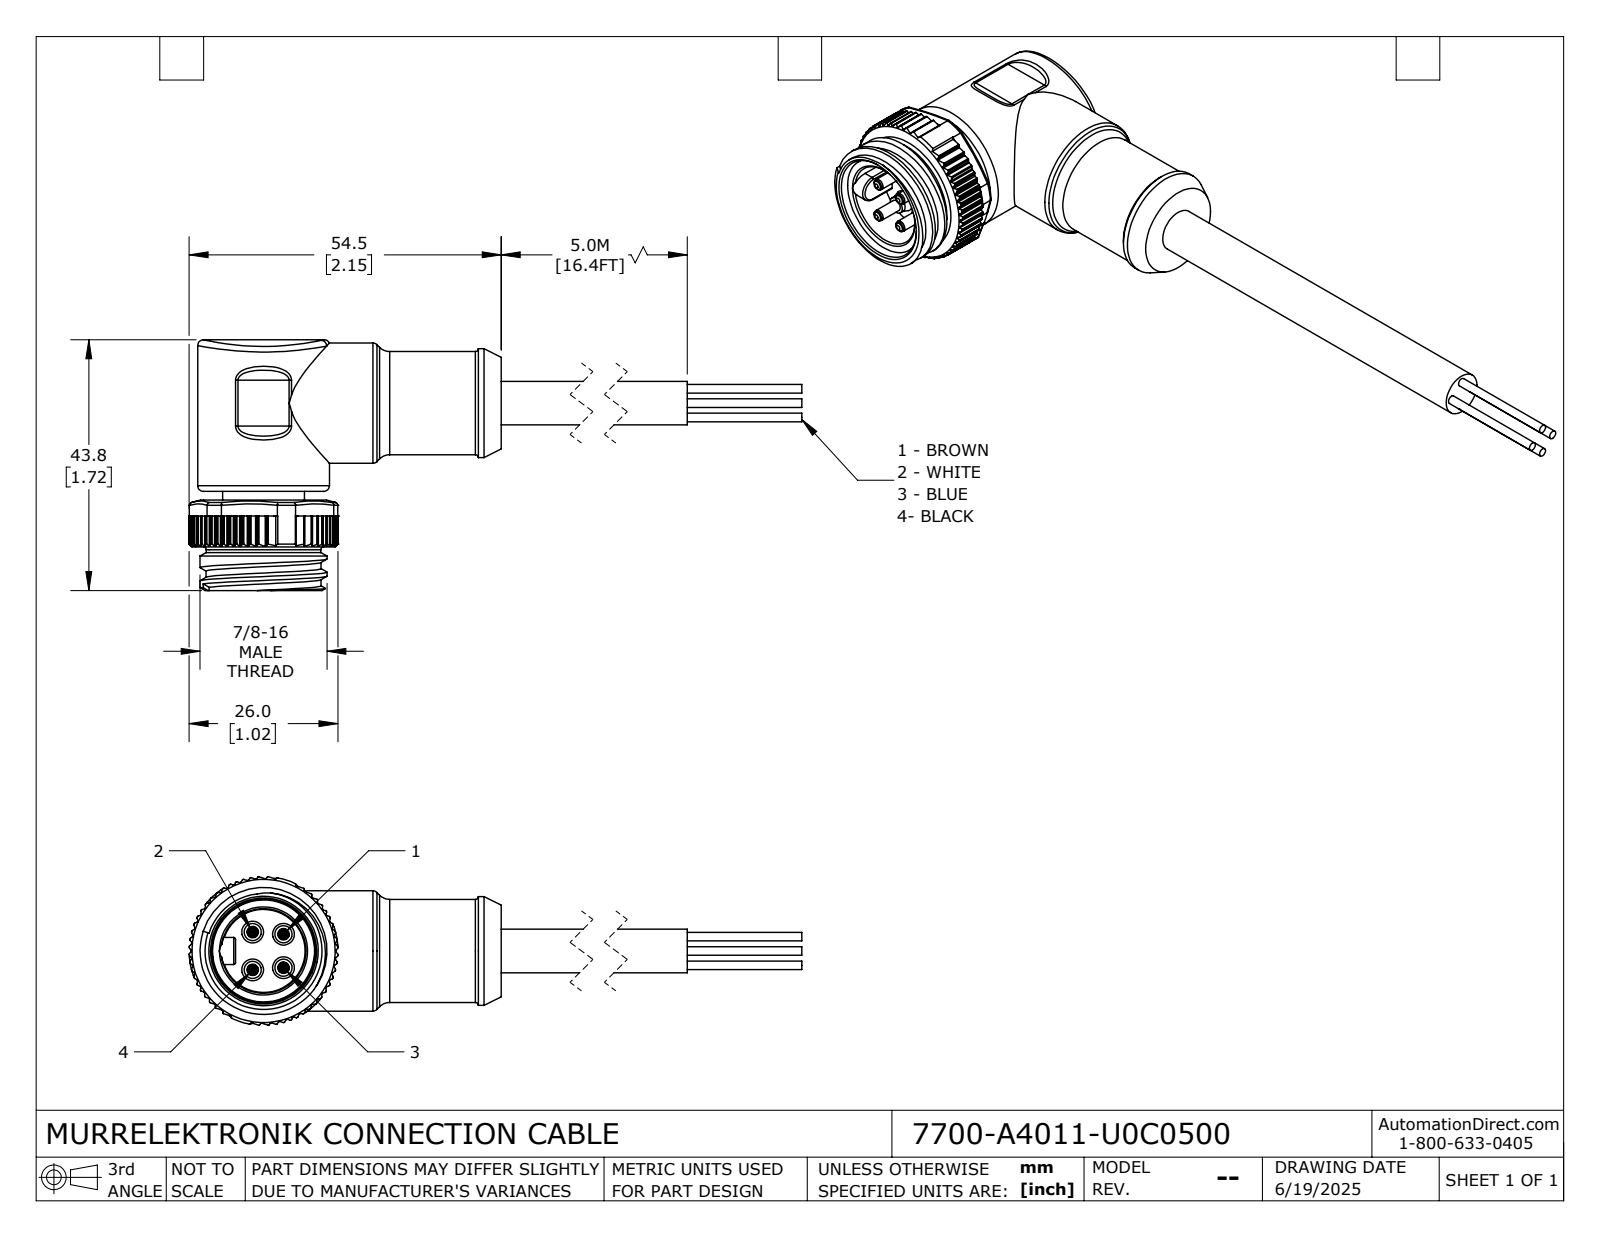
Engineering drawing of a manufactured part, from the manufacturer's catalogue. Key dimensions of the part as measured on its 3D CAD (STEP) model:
Part name (STEP PRODUCT): 7700-A4011-U0C0500
STEP written by: SolidWorks 2024 (CONFIG_CONTROL_DESIGN)
Units: millimetres
Bodies: 1 solid, 604 faces (238 planar, 282 cylindrical, 84 other)
Overall size (bounding box): 144.49 × 43.76 × 25.95
Volume: 28 280 mm³ · Surface area: 10 856 mm²
Round holes (diameter × count): ⌀15.6 ×1, ⌀18.5 ×1
Round bosses / shafts (diameter × count): ⌀3 ×4, ⌀2 ×4, ⌀1.5 ×4, ⌀23 ×1, ⌀22.17 ×1, ⌀21 ×1, ⌀20.05 ×1, ⌀20 ×1
Partial cylindrical surfaces — rounded edges, fillets, slot ends (radius × count): R0.2 ×126, R0.3 ×18, R0.1 ×4, R0.7 ×4, R1 ×4, R2.5 ×4, R2.35 ×1, R13 ×1
Main face-to-face distances: 1.5, 8.2, 9.7, 0.9, 7.3, 8.8, 15.8, 21, 14.3, 6.1
